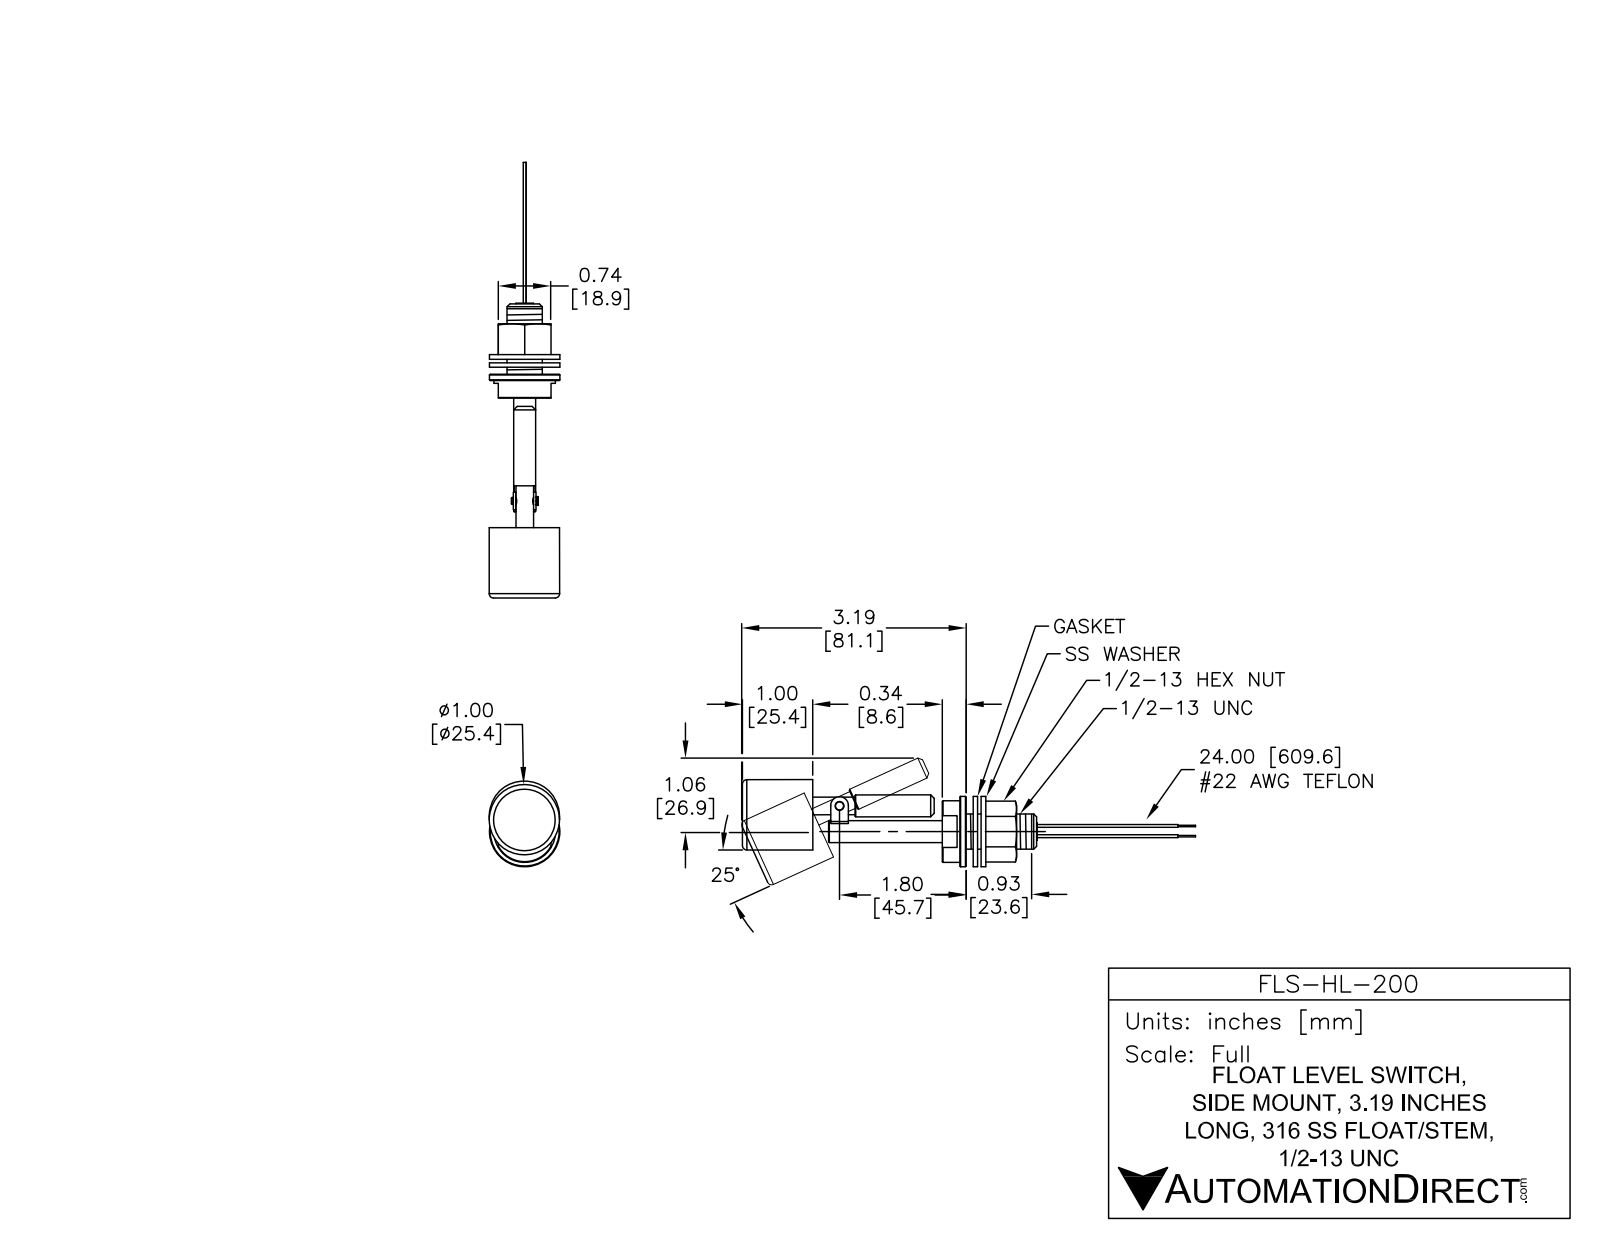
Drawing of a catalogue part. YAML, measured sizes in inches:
part_name: "FLS-HL-200"
step_written_by: "SolidWorks 2013 (AUTOMOTIVE_DESIGN)"
units: inches
bodies: {solids: 9, faces: 141, planar: 52, cylindrical: 67, other: 22}
overall_size: [6.432, 1.246, 1]
volume: 0.983
surface_area: 21.68
round_holes:
  - {diameter: 0.099, count: 1}
  - {diameter: 0.1, count: 1}
  - {diameter: 0.171, count: 1}
  - {diameter: 0.25, count: 1}
  - {diameter: 0.312, count: 1}
  - {diameter: 0.406, count: 1}
  - {diameter: 0.503, count: 1}
  - {diameter: 0.948, count: 1}
round_bosses_or_shafts:
  - {diameter: 1, count: 2}
  - {diameter: 0.04, count: 2}
  - {diameter: 0.02, count: 2}
  - {diameter: 0.875, count: 1}
  - {diameter: 0.5, count: 1}
  - {diameter: 0.312, count: 1}
  - {diameter: 0.296, count: 1}
  - {diameter: 0.25, count: 1}
partial_cylinders:
  - {radius: 0.005, count: 4}
  - {radius: 0.03, count: 2}
  - {radius: 0.12, count: 2}
  - {radius: 0.191, count: 1}
face_to_face_distances: [0.125, 0.187, 1, 3.183, 0.092, 2.399, 2.461, 2.307, 2.37, 0.062]
hole_center_spacings: [0.129, 0.246, 0.375]
